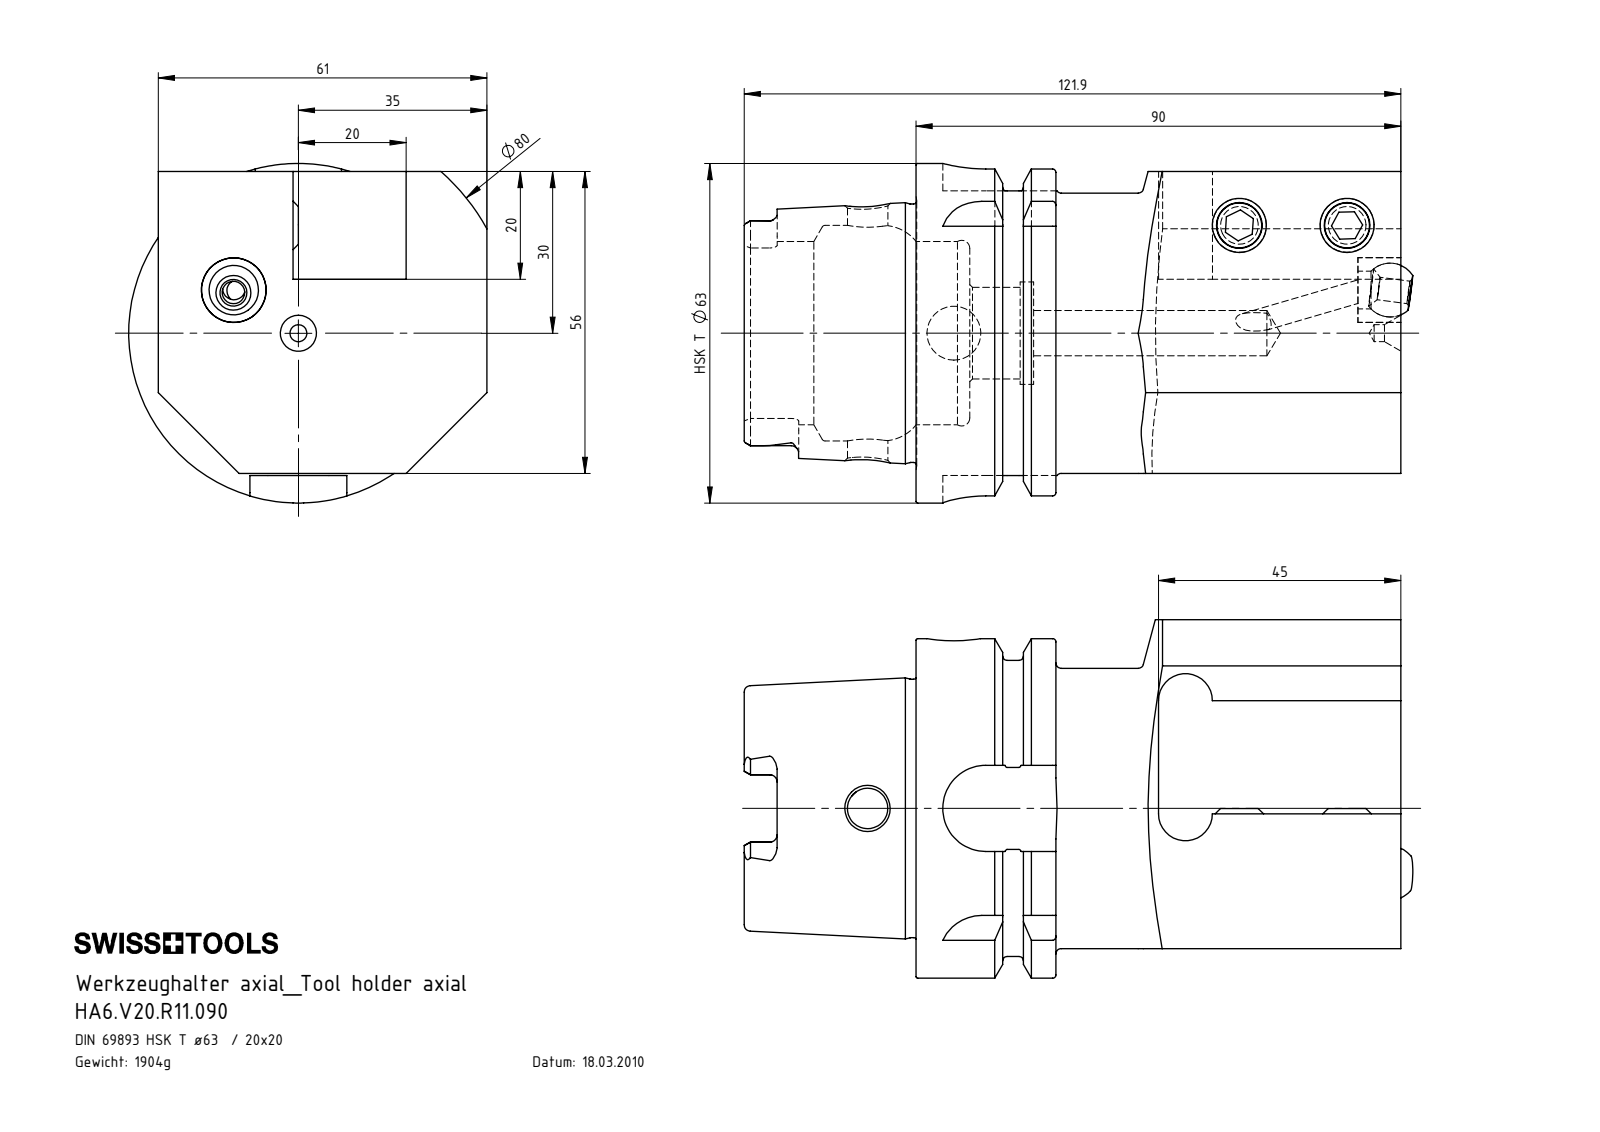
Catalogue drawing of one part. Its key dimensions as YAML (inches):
part_name: "HA6-V20.R11.090_B; HA6.V20.R11.090; KU1-U12.001.010_2; KU1-U12.001.010_1 (+2 more)"
step_written_by: "SolidWorks 2017 (AUTOMOTIVE_DESIGN)"
units: inches
bodies: {solids: 5, faces: 240, planar: 75, cylindrical: 68, other: 97}
overall_size: [4.87, 2.618, 2.48]
volume: 14.82
surface_area: 68.93
round_holes:
  - {diameter: 0.165, count: 2}
  - {diameter: 0.335, count: 2}
  - {diameter: 0.124, count: 1}
  - {diameter: 0.276, count: 1}
  - {diameter: 0.295, count: 1}
  - {diameter: 0.331, count: 1}
  - {diameter: 0.394, count: 1}
  - {diameter: 0.472, count: 1}
  - {diameter: 0.669, count: 1}
  - {diameter: 0.748, count: 1}
  - {diameter: 1.339, count: 1}
  - {diameter: 1.575, count: 1}
round_bosses_or_shafts:
  - {diameter: 0.394, count: 2}
  - {diameter: 2.48, count: 1}
  - {diameter: 2.163, count: 1}
  - {diameter: 2.047, count: 1}
  - {diameter: 1.887, count: 1}
partial_cylinders:
  - {radius: 0.055, count: 6}
  - {radius: 0.113, count: 4}
  - {radius: 0.315, count: 4}
  - {radius: 0.197, count: 2}
  - {radius: 1.575, count: 1}
face_to_face_distances: [1.417, 2.205, 2.402, 0.787, 3.543, 1.772, 0.591, 1.811, 0.984, 0.63]
hole_center_spacings: [0.568, 0.787, 2.23, 2.98]
